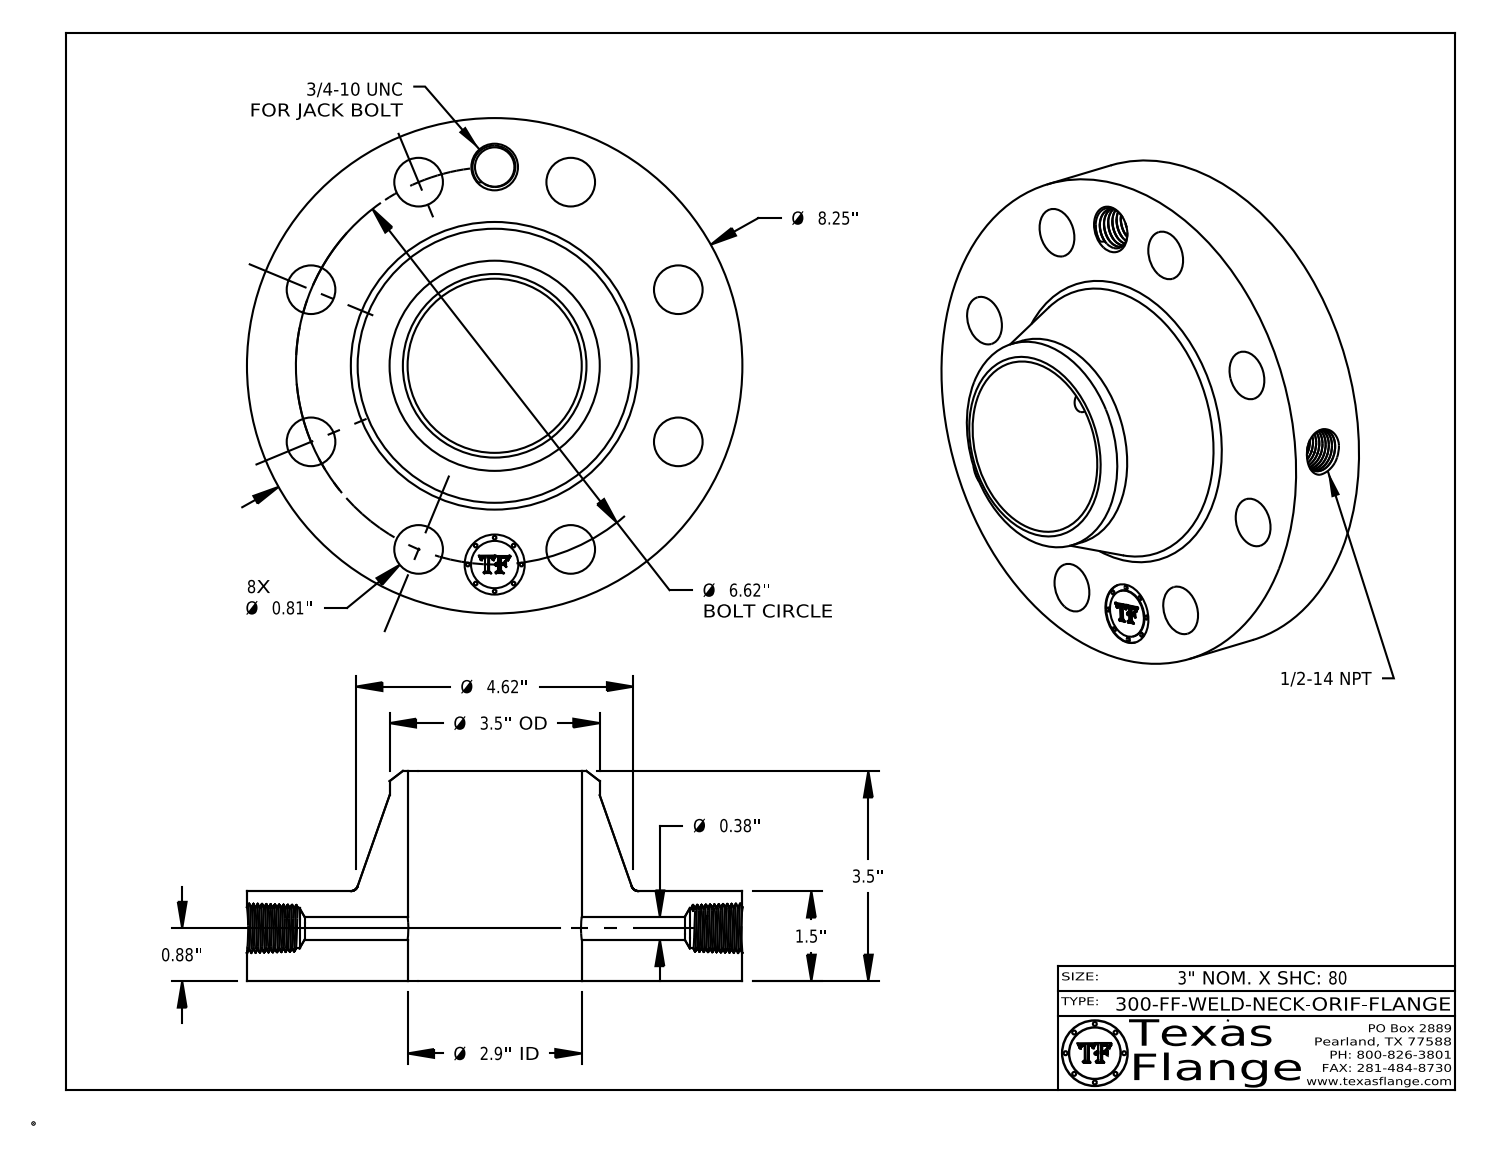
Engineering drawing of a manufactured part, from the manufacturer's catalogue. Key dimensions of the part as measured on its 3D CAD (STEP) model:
Part name (STEP PRODUCT): 300-FF-WELD-NECK
STEP written by: CATIA V5 STEP AP214 (AUTOMOTIVE_DESIGN)
Units: inches
Bodies: 1 solid, 766 faces (368 planar, 90 cylindrical, 308 other)
Overall size (bounding box): 8.25 × 8.25 × 3.5
Volume: 73.62 in³ · Surface area: 218.6 in²
Round holes (diameter × count): ⌀0.81 ×8, ⌀0.38 ×1, ⌀0.656 ×1, ⌀0.672 ×1, ⌀1 ×1, ⌀2.9 ×1
Round bosses / shafts (diameter × count): ⌀0.061 ×8, ⌀8.25 ×1, ⌀3.5 ×1, ⌀0.788 ×1
Main face-to-face distances: 1.5, 3.5, 2, 0.015, 1.485, 2.015, 0.298, 0.293, 0.054, 0.248
Hole centre spacings: 3.31, 4.681, 6.116, 6.62, 1.291, 2.533, 2.533, 3.678
